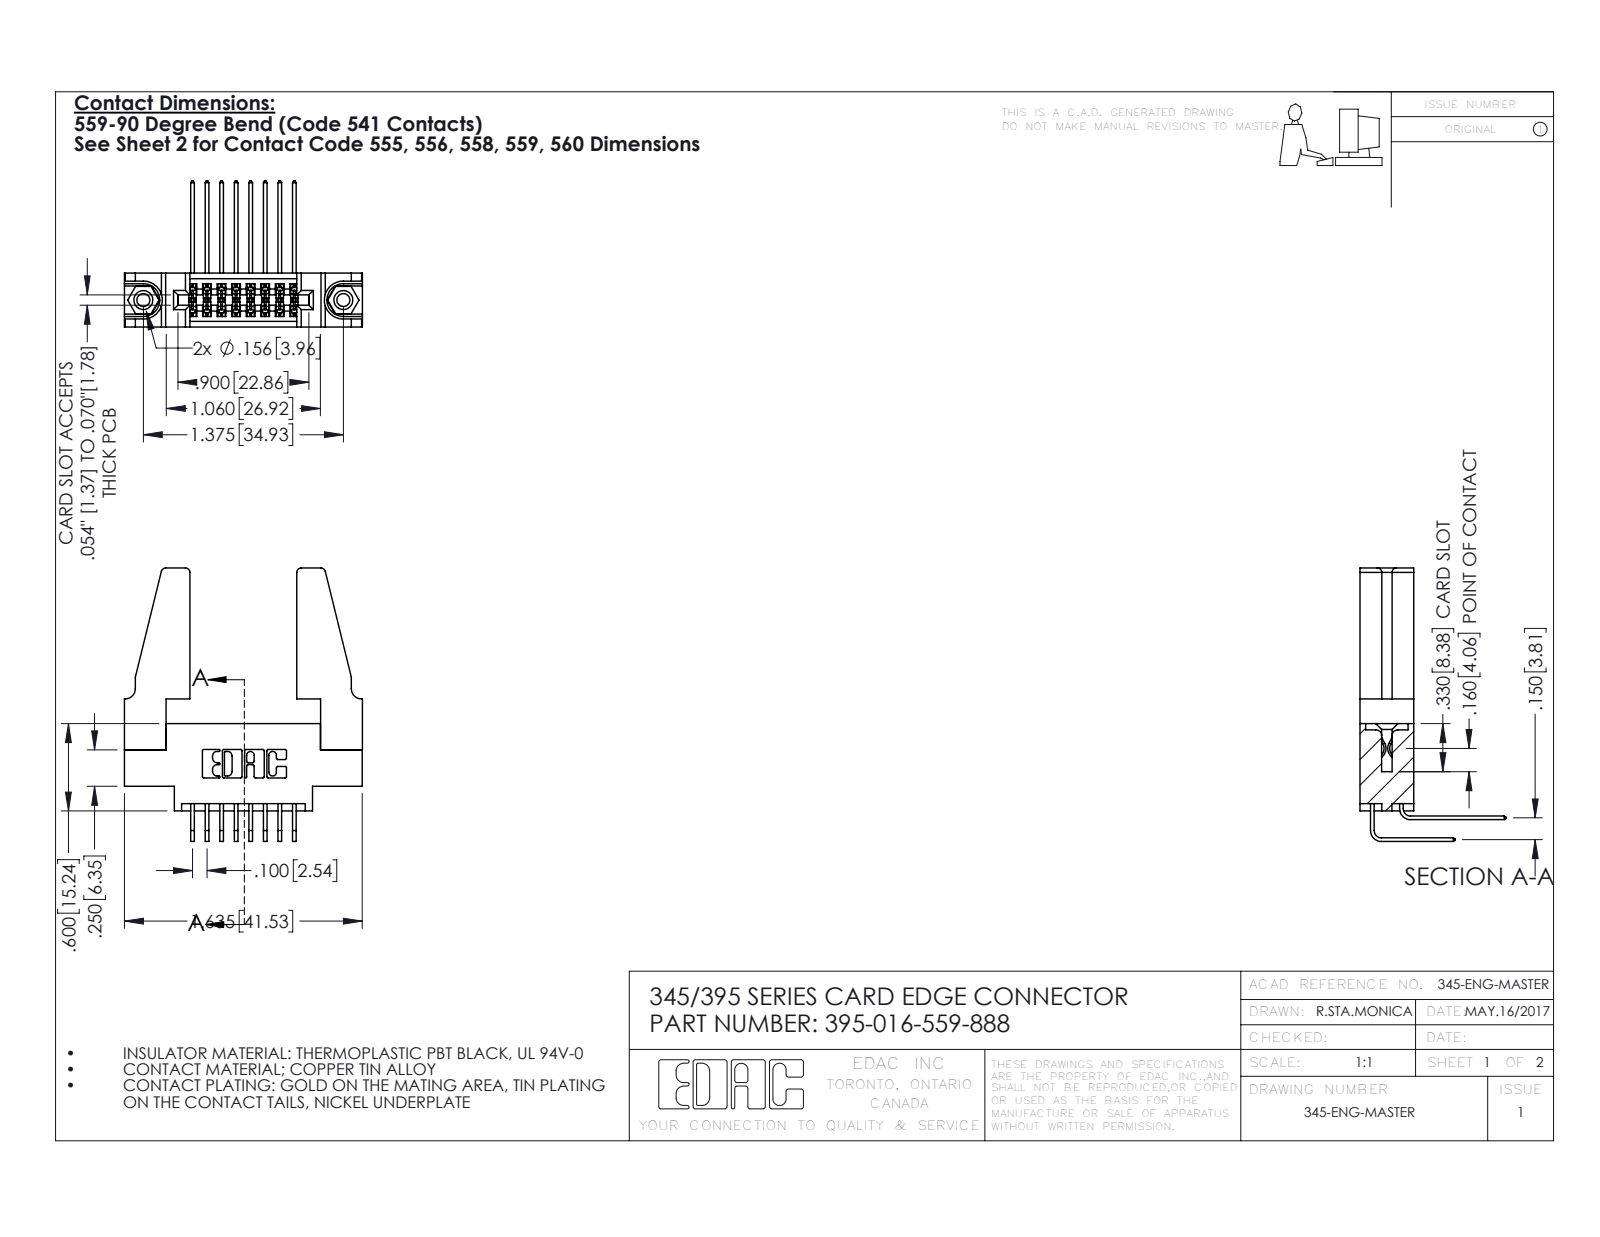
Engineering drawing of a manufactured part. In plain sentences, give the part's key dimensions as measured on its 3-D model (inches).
The part is named "395-016-559-888; 345-220-078_345-220-088; 345-292-001_558 559 Tail - 1; 345-292-001_559 Tail - 2 (+2 more)". Its 3-D file was written by "SolidWorks 2016 (CONFIG_CONTROL_DESIGN)". It is 21 solids with 1086 faces: 716 planar, 354 cylindrical and 16 other. Overall it measures 1.879 by 1.636 by 1.005 inches. Its volume is 0.424 cubic inches and its surface area 13.19 square inches. Round holes: 2 of diameter 0.089, 2 of diameter 0.125, 2 of diameter 0.156, 1 of diameter 0.064. Round bosses or shafts: 2 of diameter 0.155. Partial cylindrical surfaces (rounded edges, fillets, slot ends): 25 of radius 0.006, 22 of radius 0.01, 8 of radius 0.03, 6 of radius 0.007, 6 of radius 0.031, 3 of radius 0.026, 2 of radius 0.014, 2 of radius 0.019. The main face-to-face distances are 0.37, 0.072, 0.298, 0.15, 0.098, 0.272, 0.025, 0.2, 0.225, 0.15. The hole center spacings are 0.27, 1.144, 1.375.
